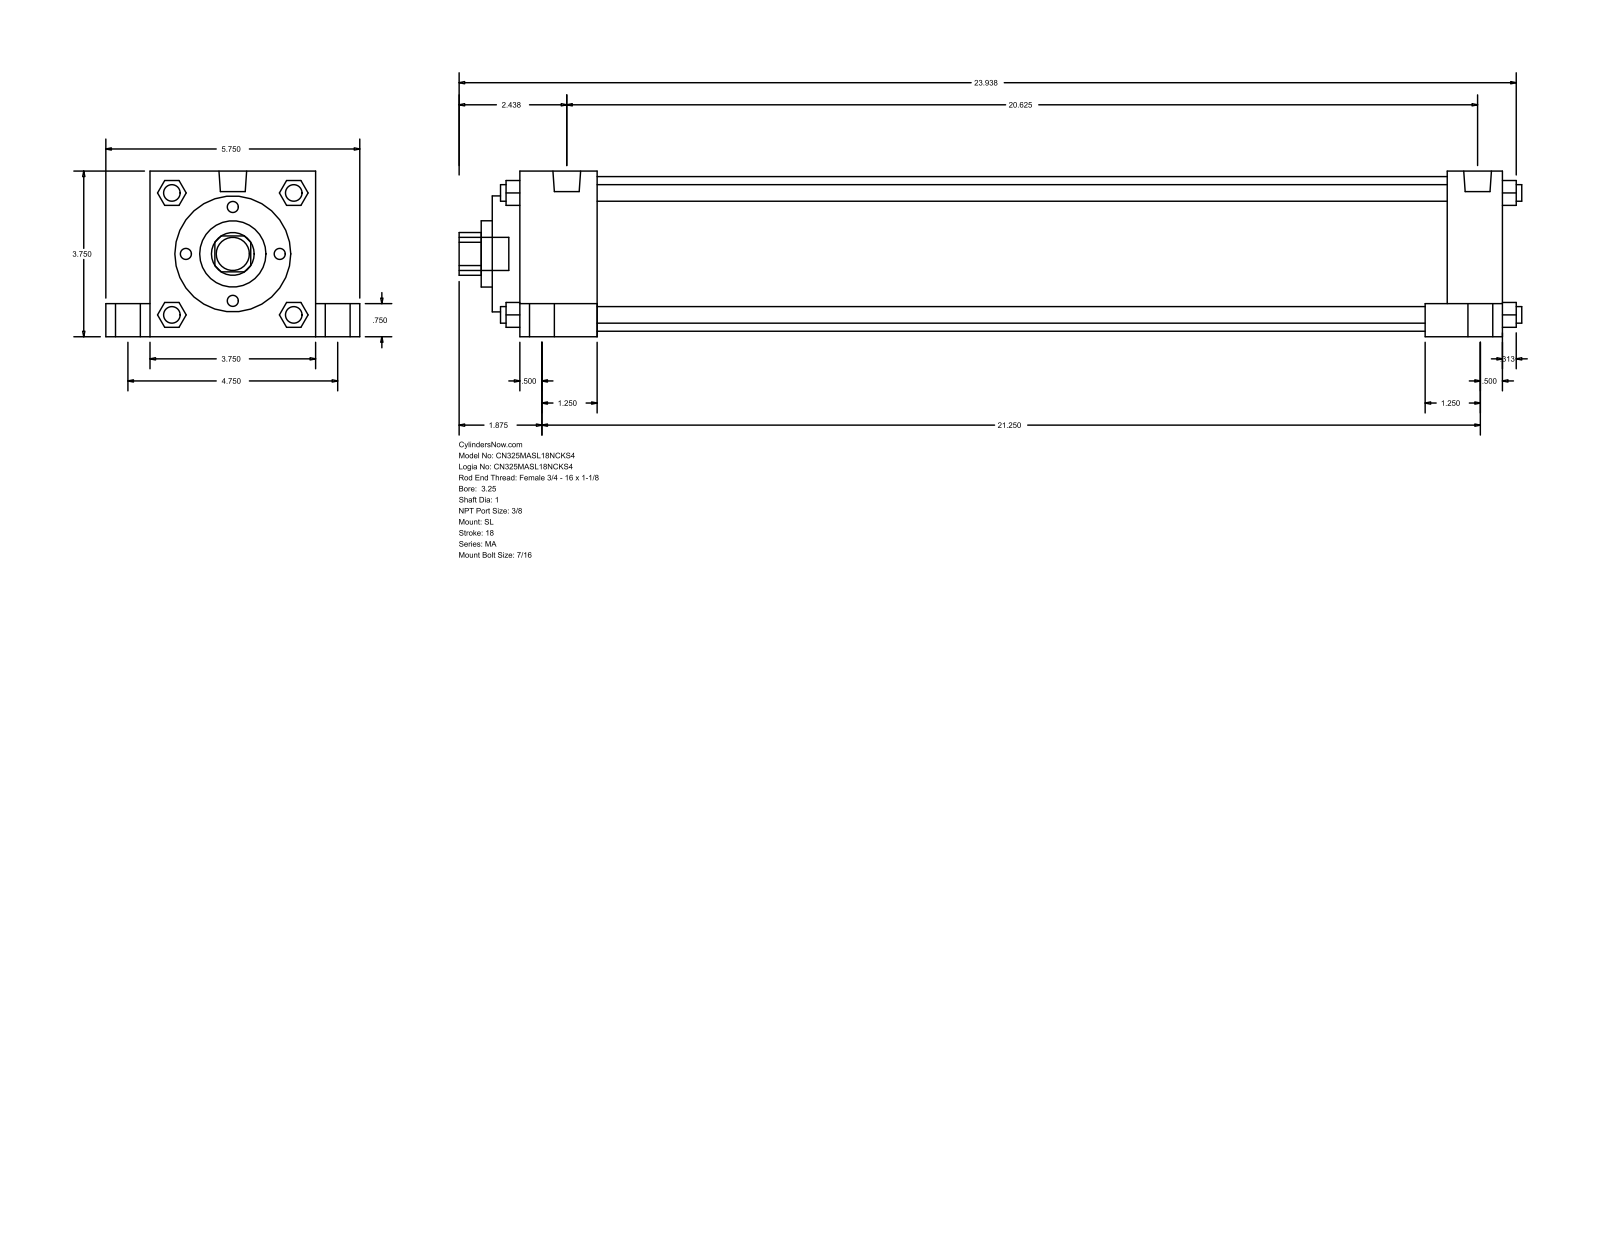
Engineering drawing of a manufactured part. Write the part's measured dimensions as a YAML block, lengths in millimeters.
part_name: "MA_SL__0325_1"
step_written_by: "GSSL Pune (CONFIG_CONTROL_DESIGN)"
units: millimeters
bodies: {solids: 0, faces: 150, planar: 113, cylindrical: 37, other: 0}
overall_size: [611.19, 146.05, 95.25]
round_holes:
  - {diameter: 25.4, count: 1}
  - {diameter: 38.1, count: 1}
  - {diameter: 66.67, count: 1}
  - {diameter: 88.9, count: 1}
round_bosses_or_shafts:
  - {diameter: 20.64, count: 4}
  - {diameter: 14.29, count: 4}
  - {diameter: 11.11, count: 4}
  - {diameter: 9.53, count: 4}
  - {diameter: 15.93, count: 2}
  - {diameter: 19.05, count: 1}
partial_cylinders:
  - {radius: 12.29, count: 1}
face_to_face_distances: [95.24, 565.16, 488.95, 15.87, 25.41, 120.65, 19.05, 533.41, 31.75, 44.46]
